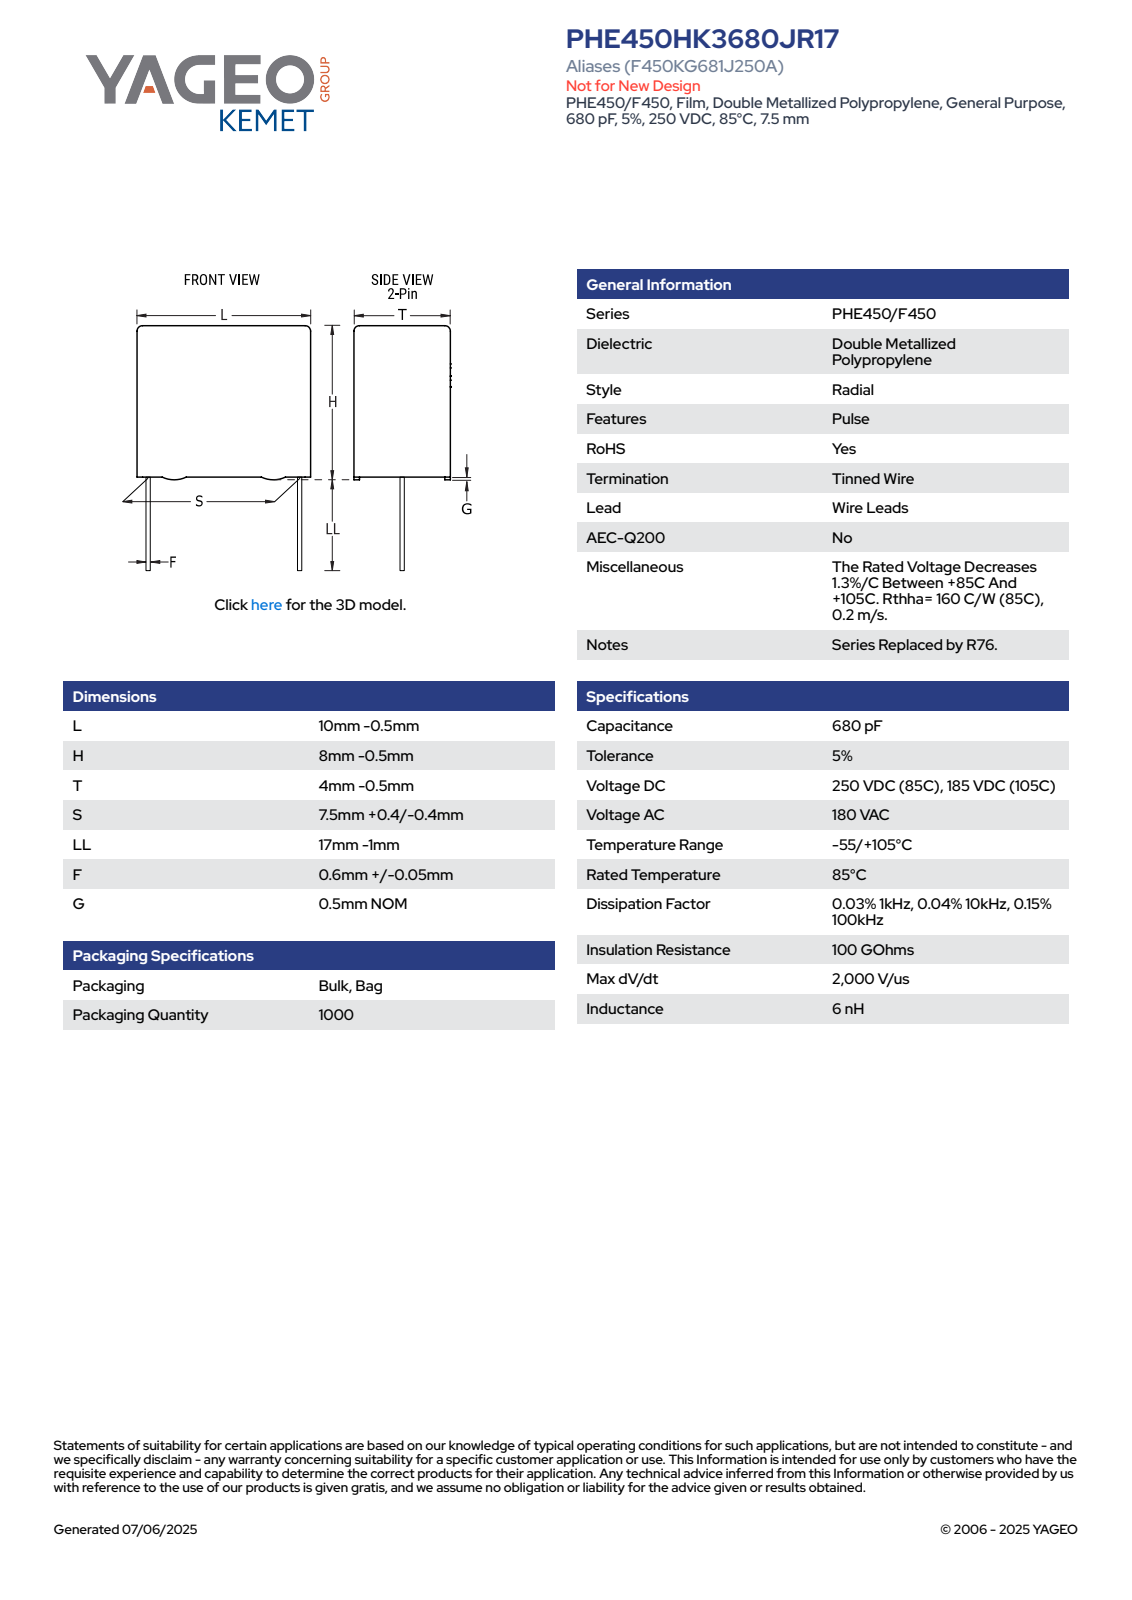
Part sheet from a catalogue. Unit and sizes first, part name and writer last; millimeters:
Units: millimetres
Overall size (bounding box): 23.5 × 9.5 × 3.5
Round bosses / shafts (diameter × count): ⌀0.65 ×2
Partial cylindrical surfaces — rounded edges, fillets, slot ends (radius × count): R0.5 ×4
Main face-to-face distances: 3.5, 9.5, 7, 3.3, 3.1, 0.5, 7.5, 16, 16.5, 23.5
Volume: 243 mm³ · Surface area: 327 mm²
Bodies: 4 solids, 89 faces (81 planar, 8 cylindrical, 0 other)
Part name (STEP PRODUCT): CFR_RBG_10X8X4_L9.5H7.5T3.5S7.5LL16F0.65G0.5
STEP written by: SolidWorks 2014 (AUTOMOTIVE_DESIGN)
